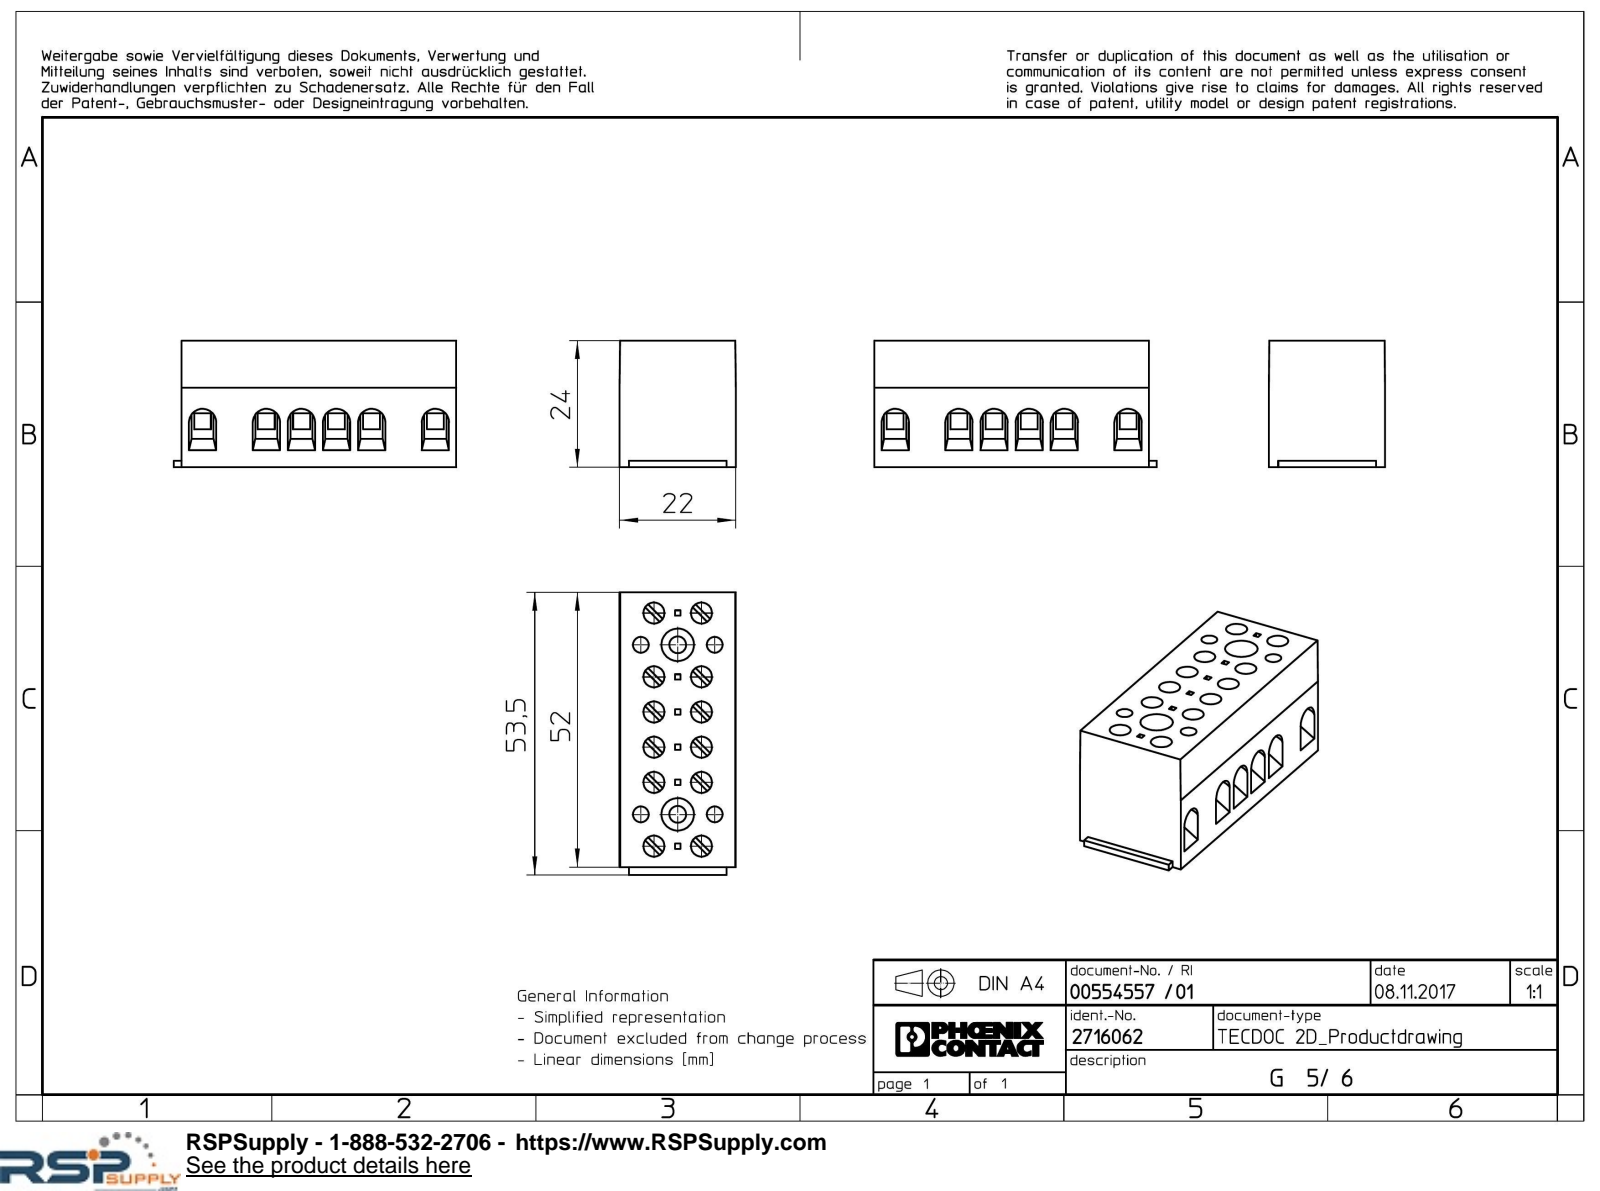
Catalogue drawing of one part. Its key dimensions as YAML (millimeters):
part_name: "G5_6-select"
step_written_by: "Creo Elements/Direct Modeling 20.1A 29-Sep-2018 (C) Parametric Technology GmbH (AUTOMOTIVE_DESIGN)"
units: millimeters
bodies: {solids: 1, faces: 331, planar: 263, cylindrical: 68, other: 0}
overall_size: [53.5, 24, 22]
volume: 22875
surface_area: 9559
round_holes:
  - {diameter: 4, count: 12}
  - {diameter: 3, count: 4}
  - {diameter: 3.2, count: 2}
  - {diameter: 6.16, count: 2}
round_bosses_or_shafts:
  - {diameter: 5, count: 2}
partial_cylinders:
  - {radius: 2.58, count: 6}
  - {radius: 0.8, count: 2}
face_to_face_distances: [23, 22, 52, 3.04, 6.18, 16.82, 9.22, 13.78, 1, 6.65]
hole_center_spacings: [6.65, 9, 11.19, 12.97, 6.5, 7, 7.5, 7.56]
